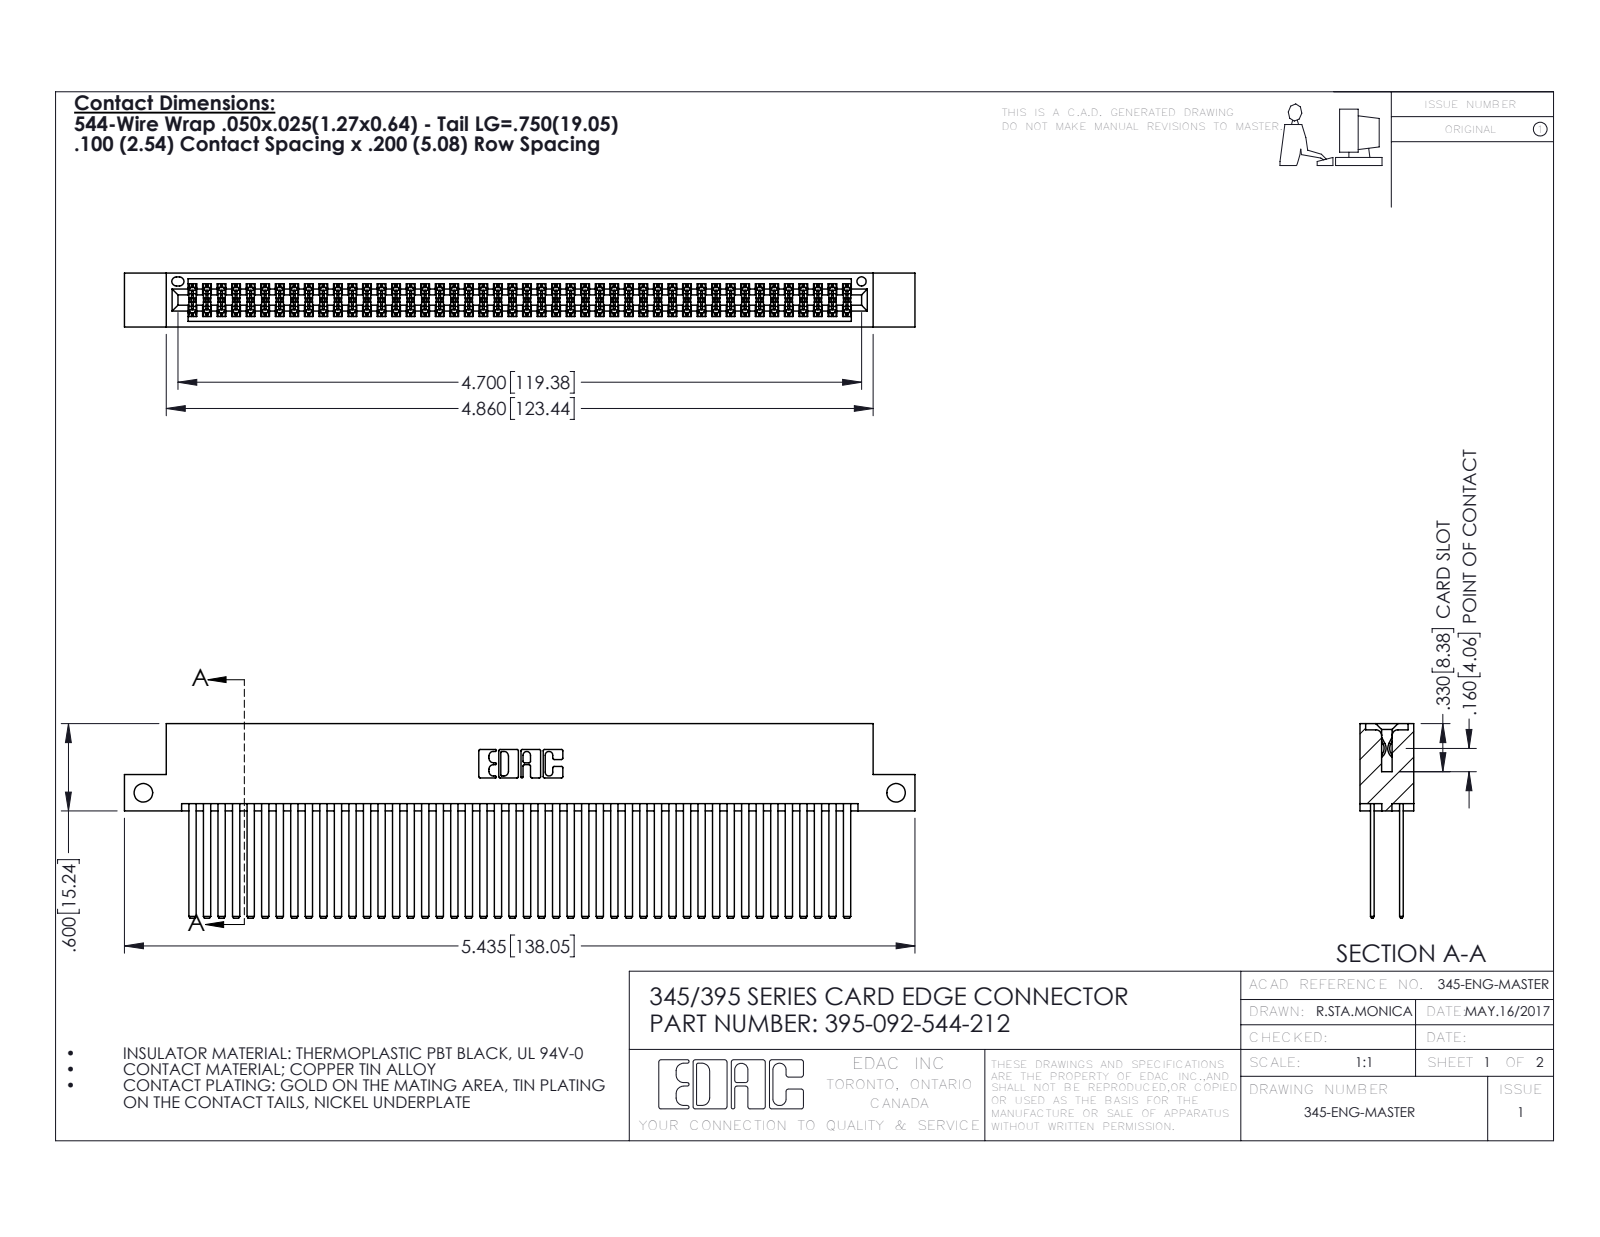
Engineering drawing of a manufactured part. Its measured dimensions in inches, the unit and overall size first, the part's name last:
Units: inches
Overall size (bounding box): 5.435 × 1.337 × 0.37
Round holes (diameter × count): ⌀0.128 ×2, ⌀0.064 ×1
Partial cylindrical surfaces — rounded edges, fillets, slot ends (radius × count): R0.006 ×138, R0.01 ×22, R0.007 ×6, R0.031 ×6, R0.026 ×3, R0.014 ×2, R0.019 ×2, R0.022 ×2
Main face-to-face distances: 0.2, 0.025, 0.298, 0.072, 0.098, 0.272, 0.225, 0.175, 0.37, 0.05
Hole centre spacings: 5.175
Volume: 0.894 in³ · Surface area: 39.33 in²
Bodies: 93 solids, 4174 faces (2748 planar, 1426 cylindrical, 0 other)
Part name (STEP PRODUCT): 345-292-001_345-293-144; 345 Part_Flush Mounting Lugs - Side Mount; 395-092-544-212
STEP written by: SolidWorks 2016 (CONFIG_CONTROL_DESIGN)
